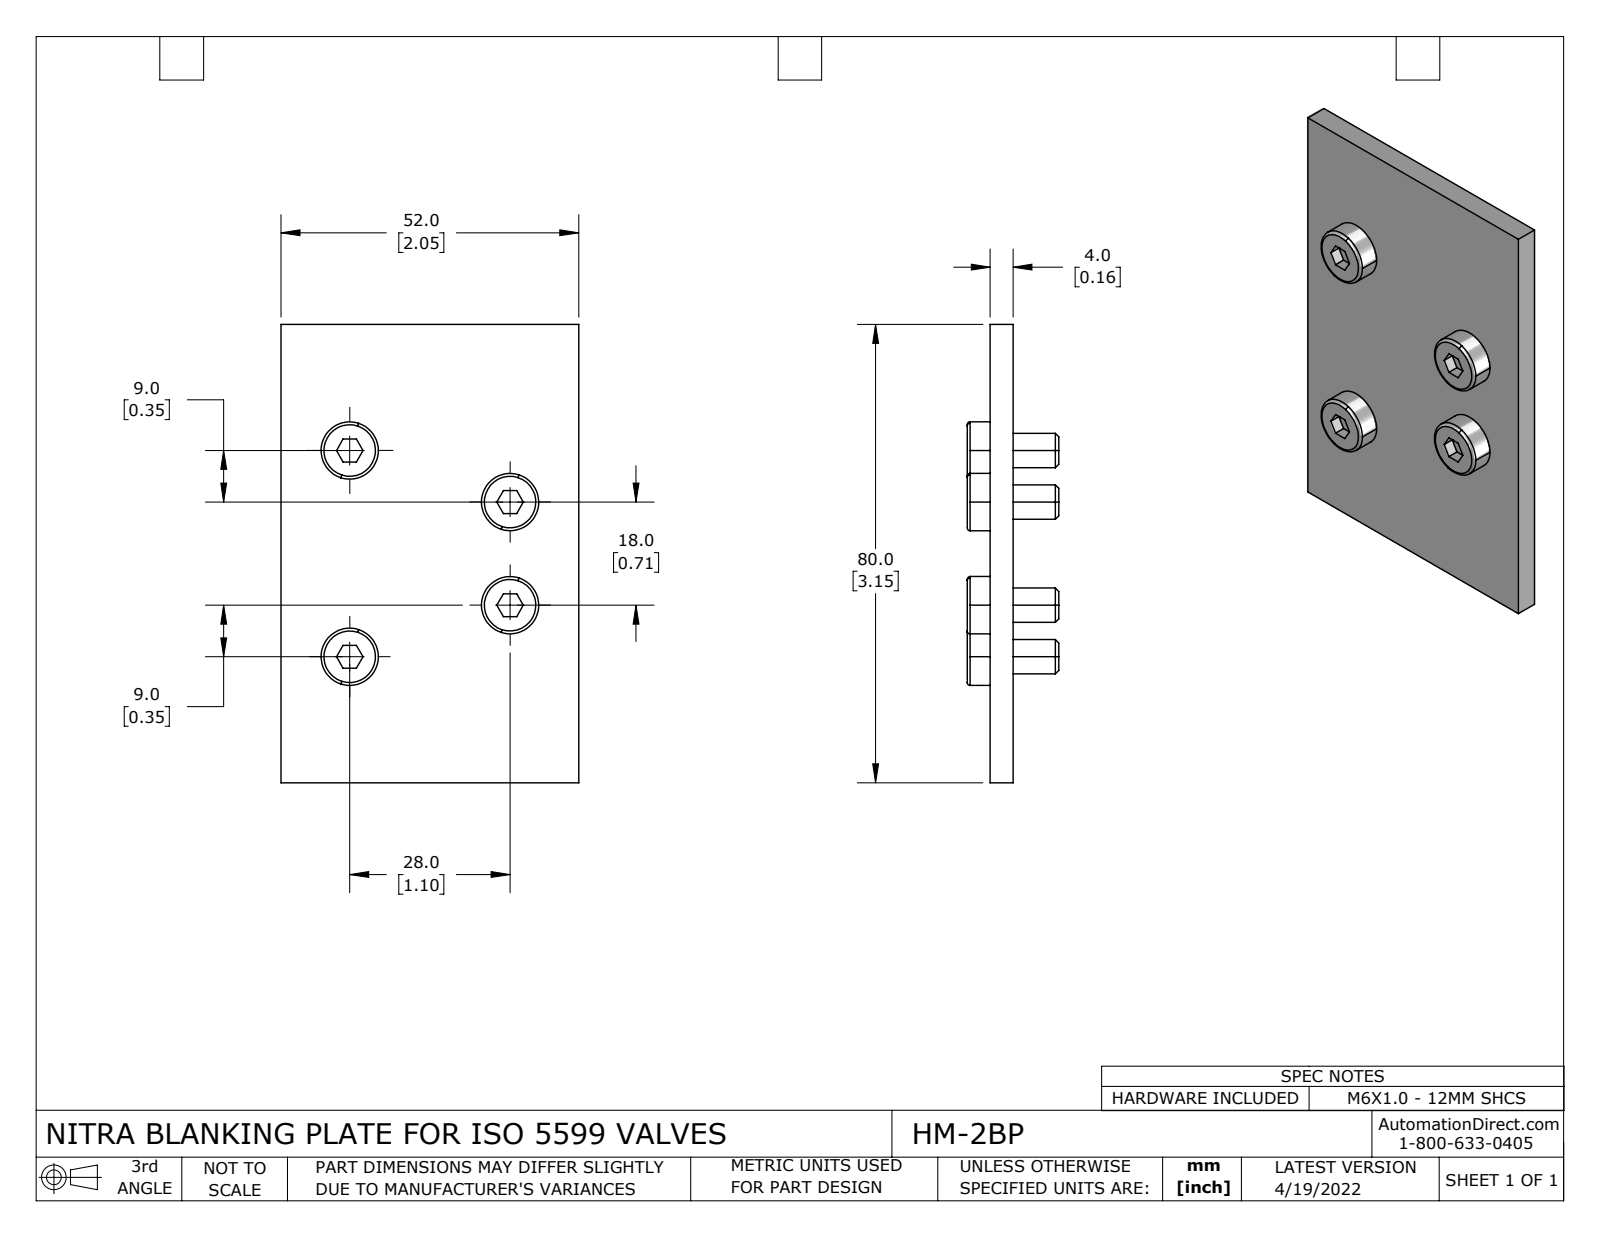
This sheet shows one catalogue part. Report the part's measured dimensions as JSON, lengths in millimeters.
{"part_name": "HM-2BP", "step_written_by": "SolidWorks 2021 (CONFIG_CONTROL_DESIGN)", "units": "millimeters", "bodies": {"solids": 1, "faces": 86, "planar": 46, "cylindrical": 24, "other": 16}, "overall_size": [80, 52, 16], "volume_mm3": 18592, "surface_area_mm2": 11165, "round_holes": [[6.5, 4]], "round_bosses_or_shafts": [[10, 4], [6, 4]], "face_to_face_distances": [4, 52, 8, 80, 2, 12, 16, 14, 6, 9], "hole_center_spacings": [29.41, 38.9, 18, 36]}
